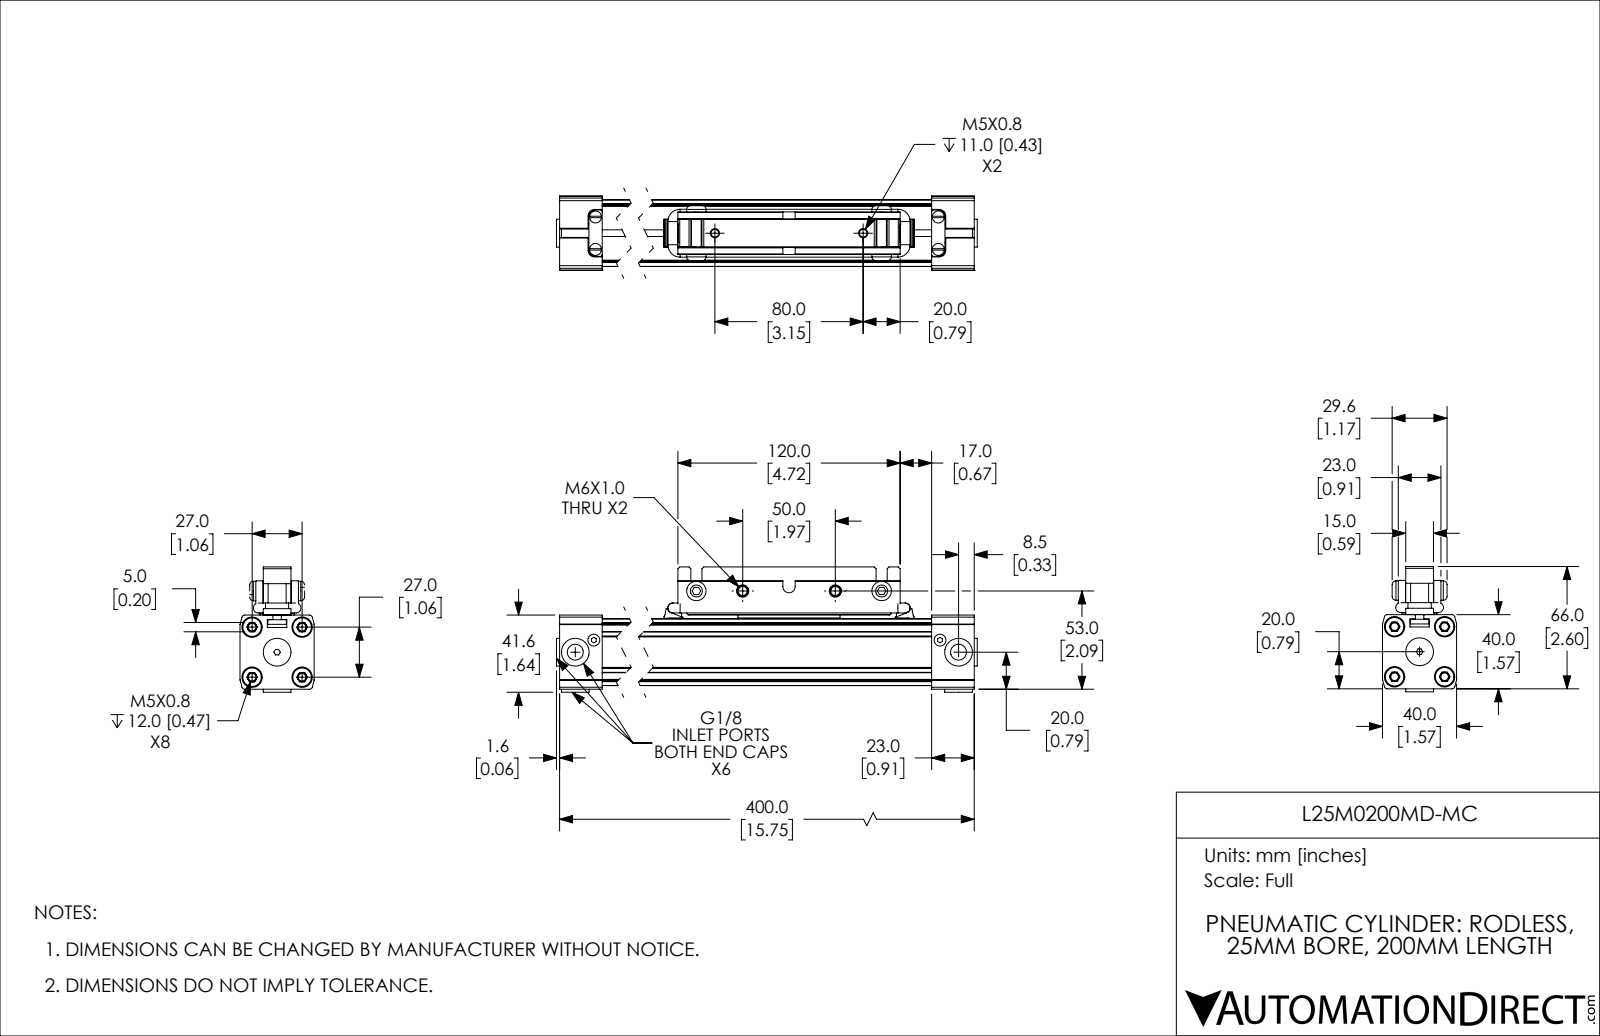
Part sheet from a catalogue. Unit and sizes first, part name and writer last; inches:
Units: inches
Overall size (bounding box): 15.877 × 2.663 × 1.575
Round holes (diameter × count): ⌀0.163 ×6, ⌀0.337 ×5, ⌀0.591 ×5, ⌀0.256 ×4, ⌀0.26 ×4, ⌀0.433 ×4, ⌀0.194 ×2, ⌀0.194 ×2, ⌀0.252 ×2, ⌀0.988 ×1
Round bosses / shafts (diameter × count): ⌀0.394 ×4, ⌀0.383 ×3, ⌀0.323 ×3, ⌀0.413 ×2, ⌀0.21 ×2, ⌀0.21 ×2, ⌀0.984 ×1
Partial cylindrical surfaces — rounded edges, fillets, slot ends (radius × count): R0.012 ×28, R0.02 ×14, R0.039 ×14, R0.01 ×12, R0.138 ×8, R0.025 ×6, R0.059 ×6, R0.094 ×6
Main face-to-face distances: 1.413, 1.417, 0.429, 0.079, 0.335, 0.906, 1.496, 0.717, 0.254, 1.159
Hole centre spacings: 0.55, 0.752, 1.063, 14.654, 0.47, 0.689, 0.698, 0.809
Volume: 27.46 in³ · Surface area: 246.9 in²
Bodies: 13 solids, 883 faces (453 planar, 322 cylindrical, 108 other)
Part name (STEP PRODUCT): L25M0200MD-MC_PISTON; L25M0200MD-MC_BODY; L25M0200MD-MC
STEP written by: SolidWorks 2019 (CONFIG_CONTROL_DESIGN)
